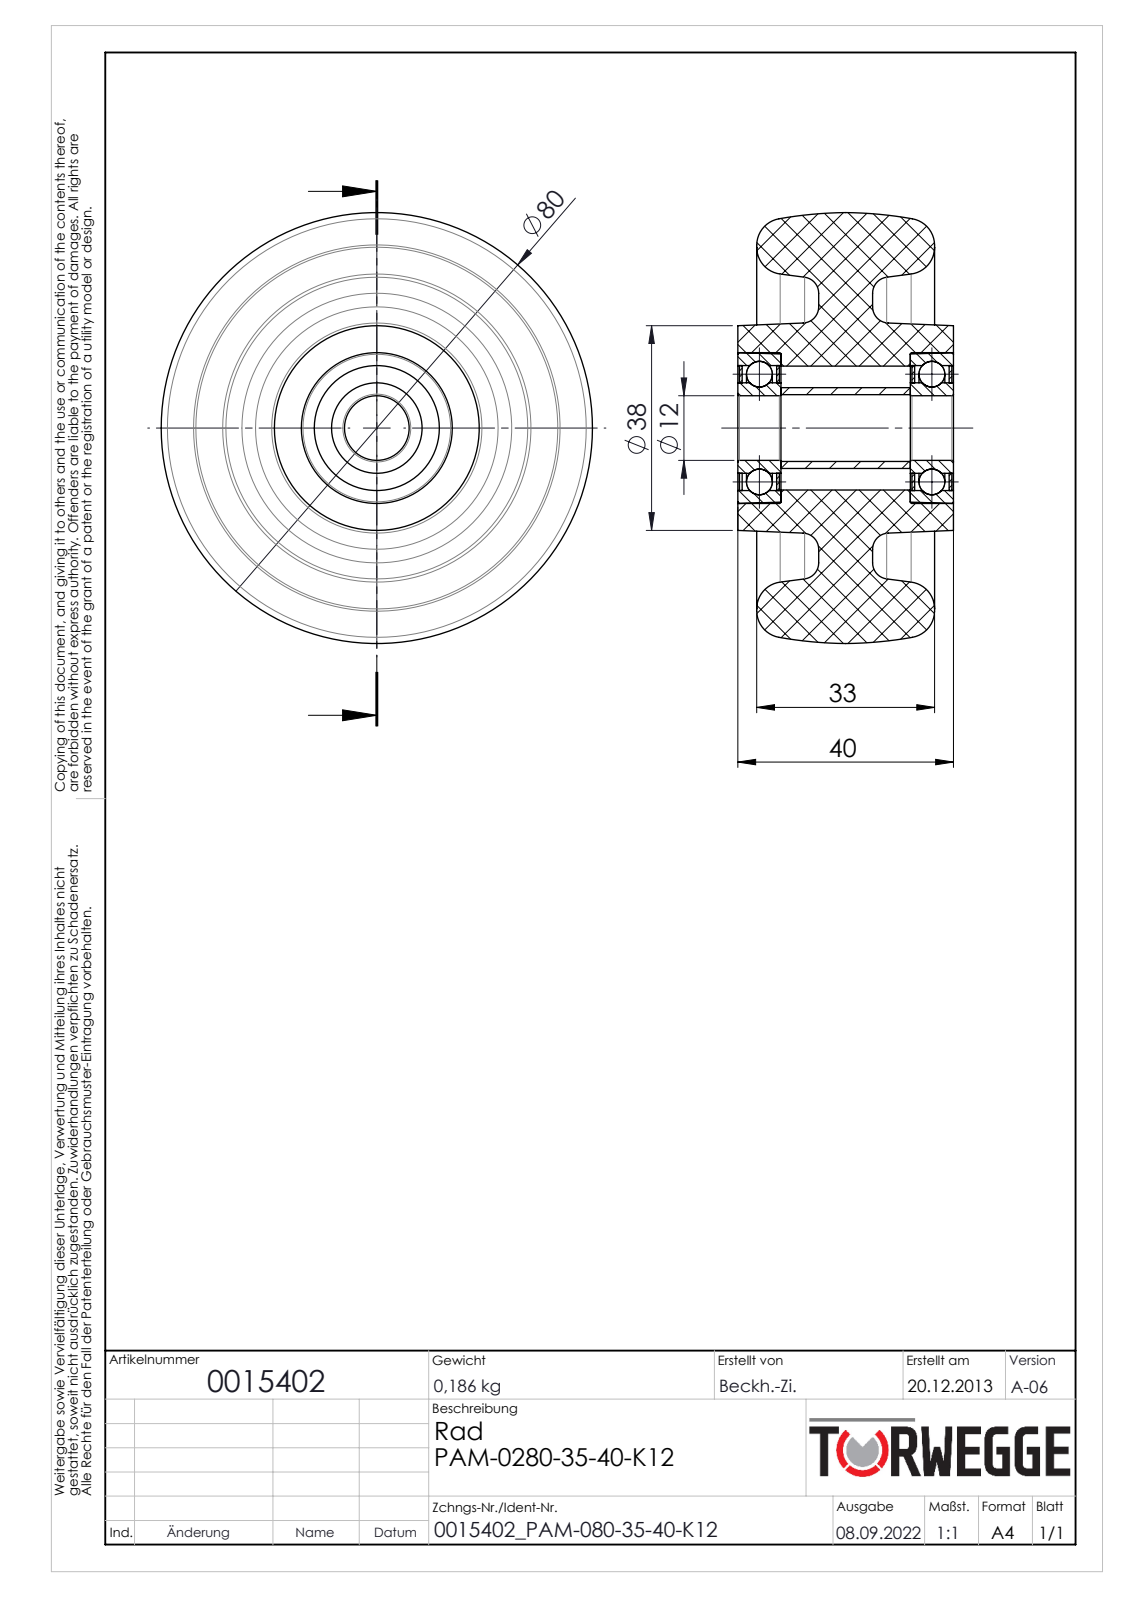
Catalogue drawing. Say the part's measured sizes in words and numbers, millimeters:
The part is named "0015402". Its 3-D file was written by "SolidWorks 2020 (AUTOMOTIVE_DESIGN)". It is 12 solids with 142 faces: 24 planar, 46 cylindrical and 72 other. Overall it measures 80 by 80 by 40 millimeters. Its volume is 123 604 cubic millimeters and its surface area 36 045 square millimeters. Round holes: 1 of diameter 12, 1 of diameter 12.4, 1 of diameter 16.8, 1 of diameter 23, 1 of diameter 23.2. Round bosses or shafts: 1 of diameter 28, 1 of diameter 15. The main face-to-face distances are 32, 8, 0.8, 7.2, 7.7, 0.5, 6.9, 40, 15, 25.
